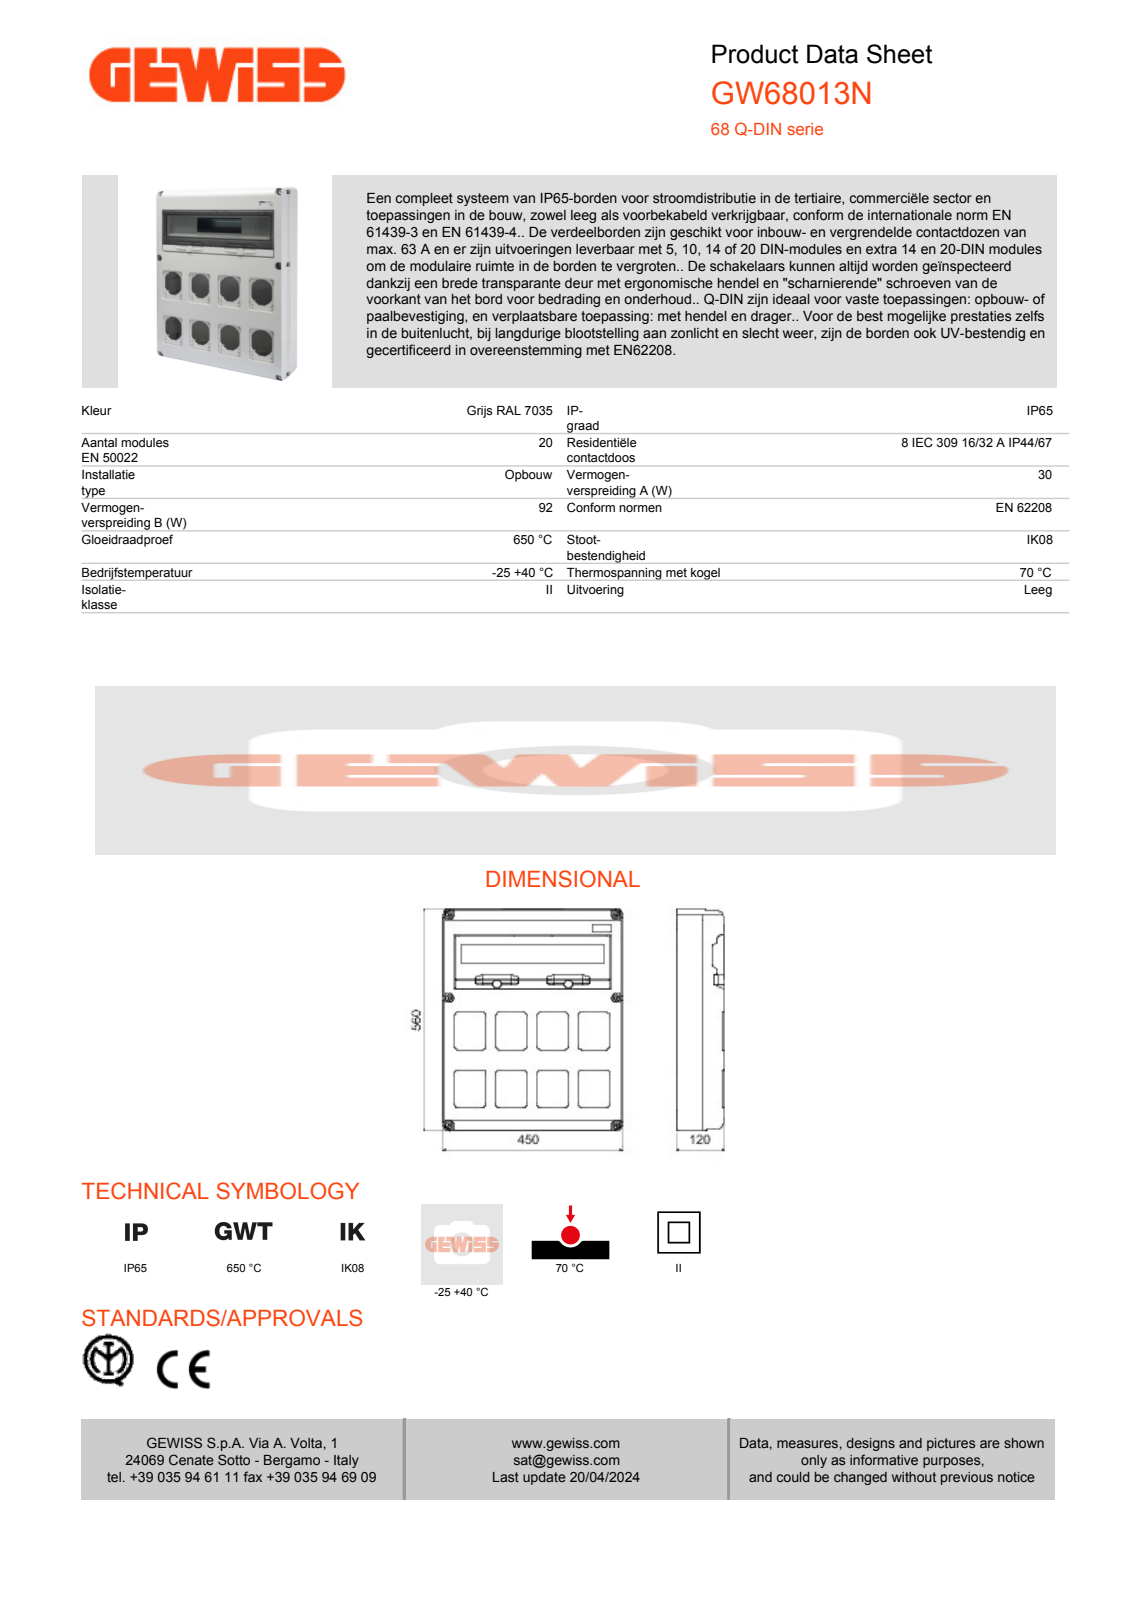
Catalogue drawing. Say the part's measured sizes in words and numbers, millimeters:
The part is named "55523526CXXX___FONDO_QDIN_20M; 55523559GXXX_FRONTALE_QDIN_20M; GW68013N_ASM". Its 3-D file was written by "CREO PARAMETRIC BY PTC INC, 2020074 (CONFIG_CONTROL_DESIGN)". It is 2 solids with 1770 faces: 923 planar, 299 cylindrical and 548 other. Overall it measures 560 by 450 by 126.02 millimeters. Its volume is 4 230 000 cubic millimeters and its surface area 1 580 000 square millimeters. Partial cylindrical surfaces (rounded edges, fillets, slot ends): 96 of radius 0.3, 32 of radius 2, 20 of radius 1.8, 16 of radius 36.5, 12 of radius 1.5, 12 of radius 1294.75, 8 of radius 2.3, 8 of radius 3. The main face-to-face distances are 3, 115.3, 118.3, 112.3, 3.07, 5.5, 109.8, 442.69, 439.62, 8.5.
